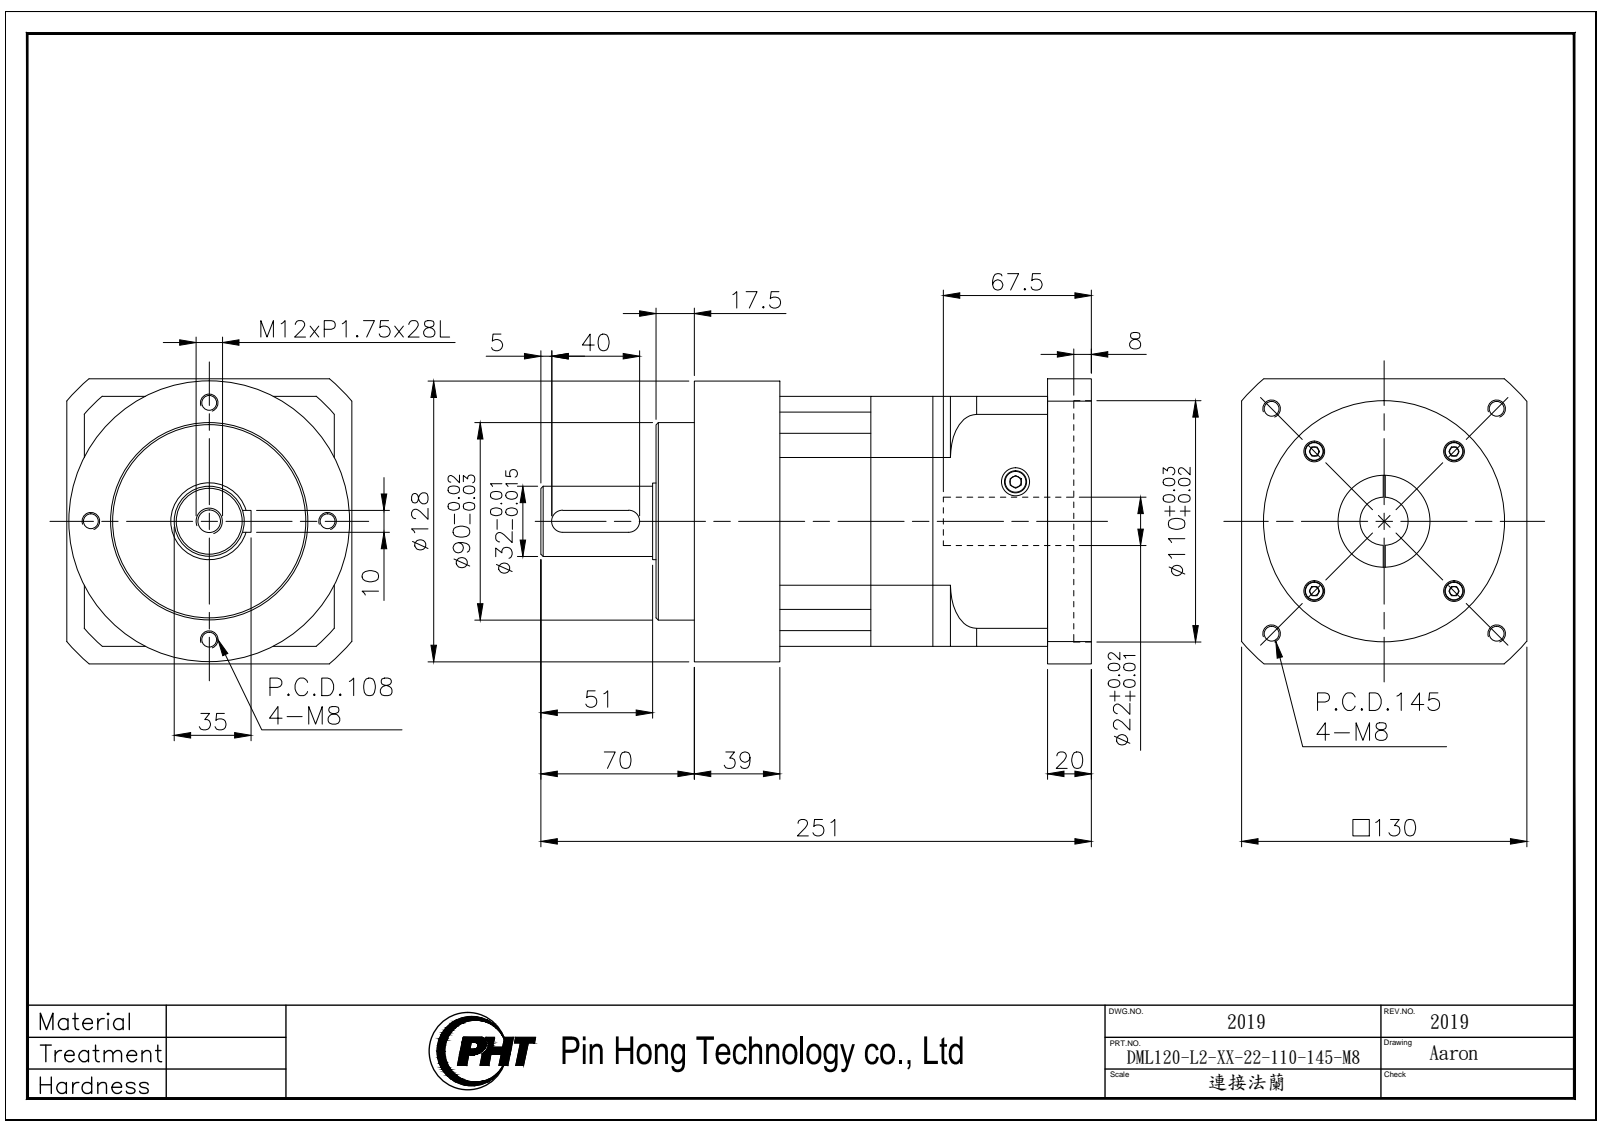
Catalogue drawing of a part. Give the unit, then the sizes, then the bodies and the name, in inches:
Units: inches
Overall size (bounding box): 9.882 × 5.118 × 5.118
Round holes (diameter × count): ⌀0.374 ×12, ⌀0.209 ×8, ⌀0.268 ×8, ⌀0.197 ×4, ⌀0.217 ×4, ⌀0.5 ×2, ⌀0.402 ×1, ⌀0.866 ×1, ⌀1.654 ×1, ⌀2.362 ×1, ⌀2.756 ×1, ⌀4.331 ×1
Round bosses / shafts (diameter × count): ⌀0.335 ×12, ⌀5.039 ×1, ⌀3.543 ×1, ⌀1.929 ×1, ⌀1.378 ×1, ⌀1.26 ×1
Partial cylindrical surfaces — rounded edges, fillets, slot ends (radius × count): R0.276 ×4, R0.197 ×2, R2.953 ×1, R3.346 ×1
Main face-to-face distances: 2.744, 1.114, 1.63, 4.488, 0.315, 4.803, 2.531, 3.646, 5.276, 2.224
Hole centre spacings: 2.323, 0.765, 0.857, 1.167, 1.527, 2.021, 2.231, 2.531
Volume: 138 in³ · Surface area: 378.6 in²
Bodies: 4 solids, 386 faces (173 planar, 157 cylindrical, 56 other)
Part name (STEP PRODUCT): DML120-L2-XX-22-110-145-M8_2019
STEP written by: SolidWorks 2016 (AUTOMOTIVE_DESIGN)
